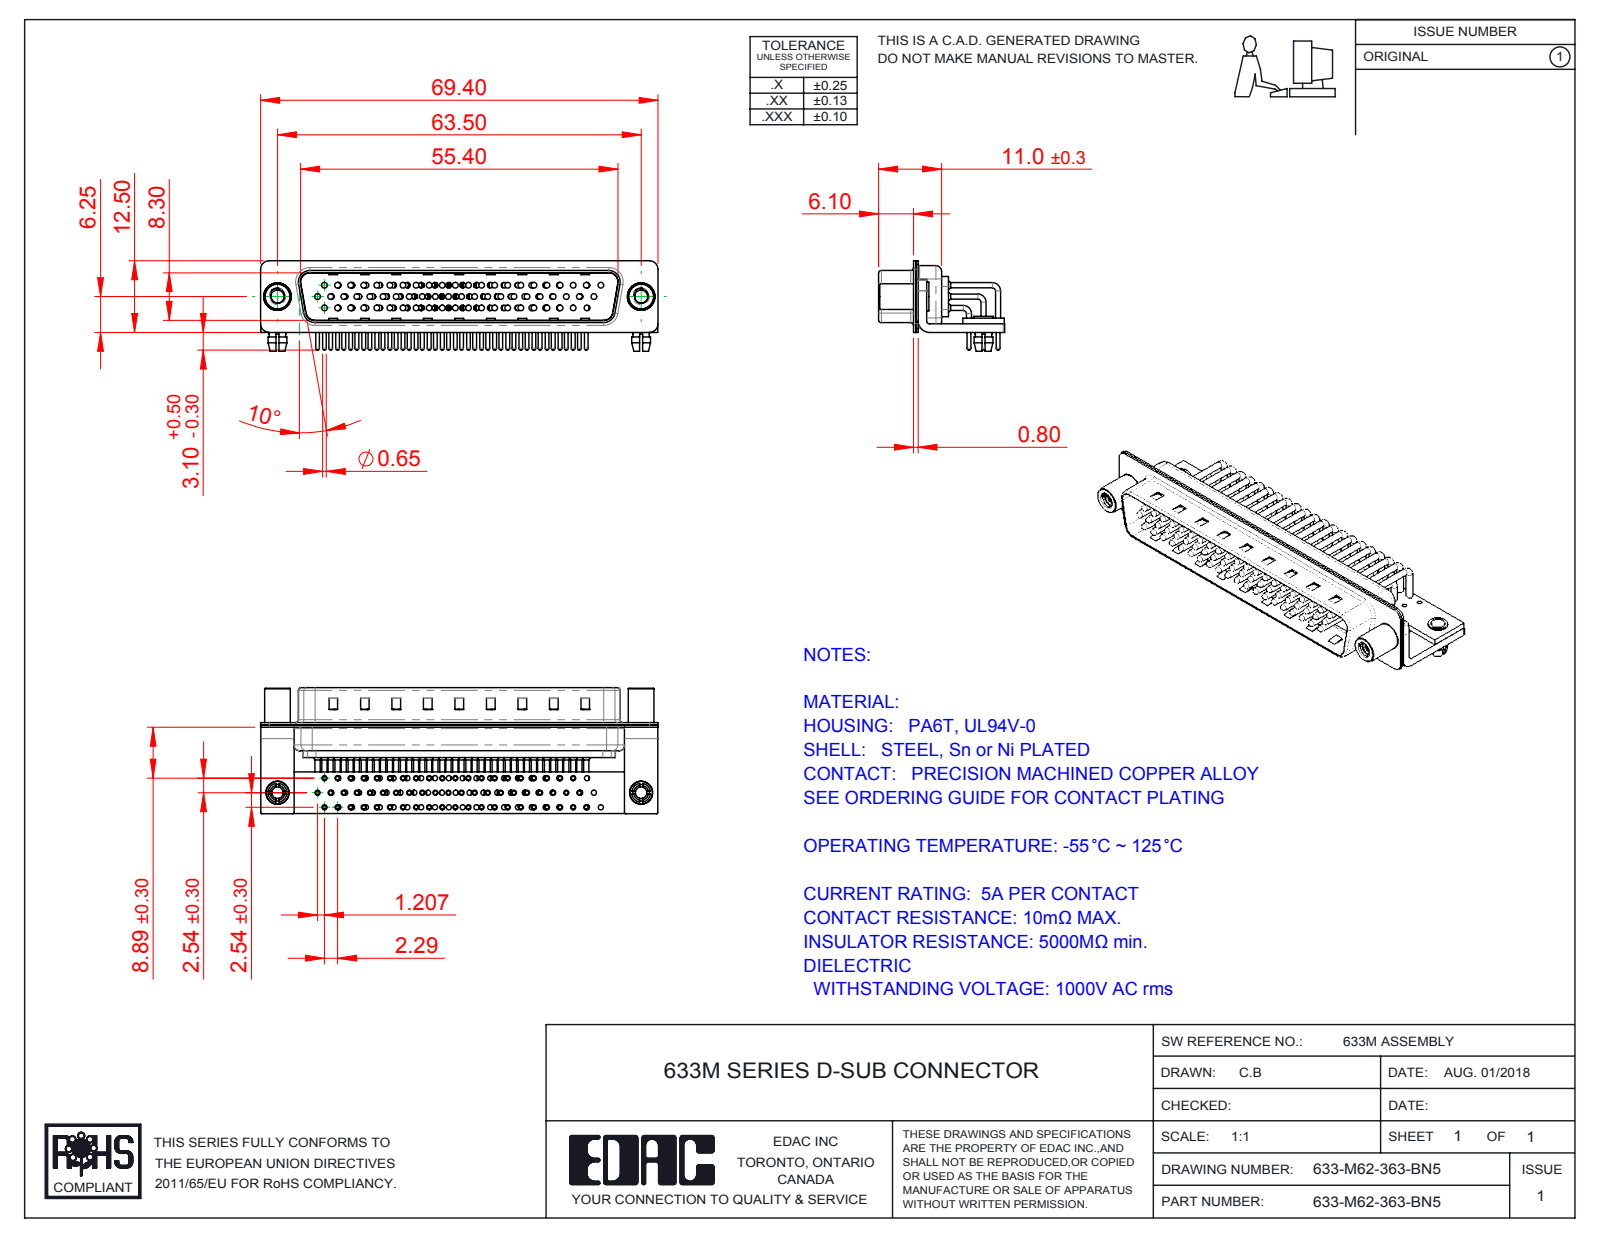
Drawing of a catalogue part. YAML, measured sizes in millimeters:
part_name: "633M Shell Front_62 Contacts; 633M 4-40 Threaded Standoff; 633M Stabilizer Board_62 Contacts; 633M Housing_62 Contacts (+7 more)"
step_written_by: "SolidWorks 2016 (CONFIG_CONTROL_DESIGN)"
units: millimeters
bodies: {solids: 72, faces: 7548, planar: 4247, cylindrical: 2593, other: 708}
overall_size: [69.4, 22, 15.8]
volume: 5247
surface_area: 16062
round_holes:
  - {diameter: 2, count: 64}
  - {diameter: 0.9, count: 62}
  - {diameter: 1, count: 62}
  - {diameter: 1.7, count: 62}
  - {diameter: 2.26, count: 2}
  - {diameter: 2.5, count: 2}
  - {diameter: 3.2, count: 2}
  - {diameter: 4, count: 2}
  - {diameter: 4.8, count: 2}
round_bosses_or_shafts:
  - {diameter: 0.9, count: 118}
  - {diameter: 1.5, count: 62}
  - {diameter: 0.65, count: 62}
  - {diameter: 1, count: 56}
  - {diameter: 5, count: 2}
  - {diameter: 4.9, count: 2}
  - {diameter: 4.5, count: 2}
  - {diameter: 4, count: 2}
partial_cylinders:
  - {radius: 1.01, count: 62}
  - {radius: 0.25, count: 16}
  - {radius: 1.5, count: 16}
  - {radius: 2, count: 13}
  - {radius: 0.5, count: 9}
  - {radius: 1.6, count: 8}
  - {radius: 0.6, count: 4}
  - {radius: 0.65, count: 4}
face_to_face_distances: [0.4, 0.85, 1.25, 1.5, 9.55, 1, 1.9, 10.4, 8.3, 0.8]
hole_center_spacings: [7.24, 2.41, 9.65, 4.83, 14.48, 16.89, 2.81, 2.32]
